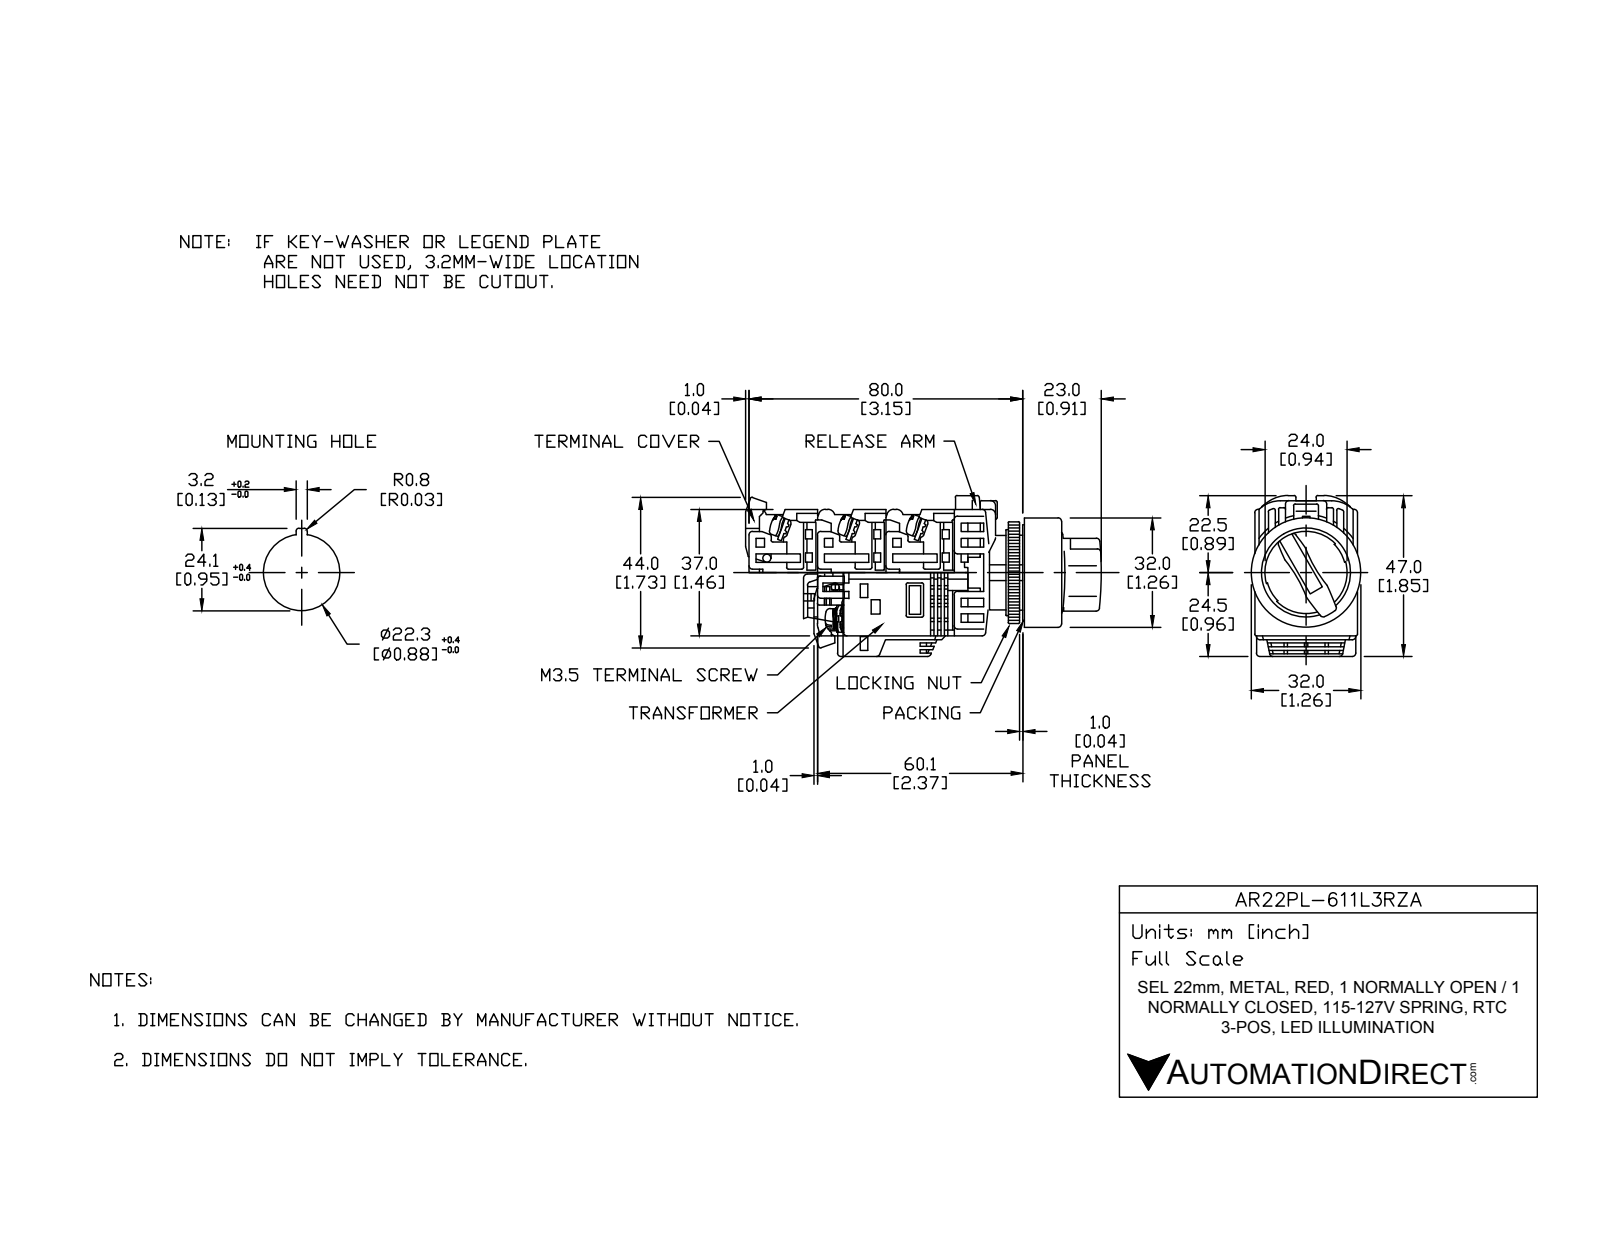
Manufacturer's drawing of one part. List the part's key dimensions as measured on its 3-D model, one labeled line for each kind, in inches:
Part name (STEP PRODUCT): AR22PL-611L3RZA
STEP written by: SolidWorks 2017 (AUTOMOTIVE_DESIGN)
Units: inches
Bodies: 23 solids, 556 faces (386 planar, 139 cylindrical, 31 other)
Overall size (bounding box): 3.327 × 1.725 × 1.26
Volume: 3.509 in³ · Surface area: 46.84 in²
Round holes (diameter × count): ⌀0.858 ×1, ⌀0.866 ×1, ⌀0.984 ×1, ⌀1.22 ×1
Round bosses / shafts (diameter × count): ⌀0.197 ×6, ⌀1.26 ×1, ⌀1.201 ×1, ⌀1.173 ×1, ⌀0.945 ×1, ⌀0.856 ×1, ⌀0.669 ×1
Partial cylindrical surfaces — rounded edges, fillets, slot ends (radius × count): R0.02 ×48, R0.069 ×8, R0.039 ×6, R0.197 ×4, R0.157 ×2, R0.472 ×1, R0.653 ×1, R0.693 ×1
Main face-to-face distances: 0.039, 0.709, 0.787, 1.142, 0.118, 1.575, 1.122, 2.697, 0.079, 0.394
